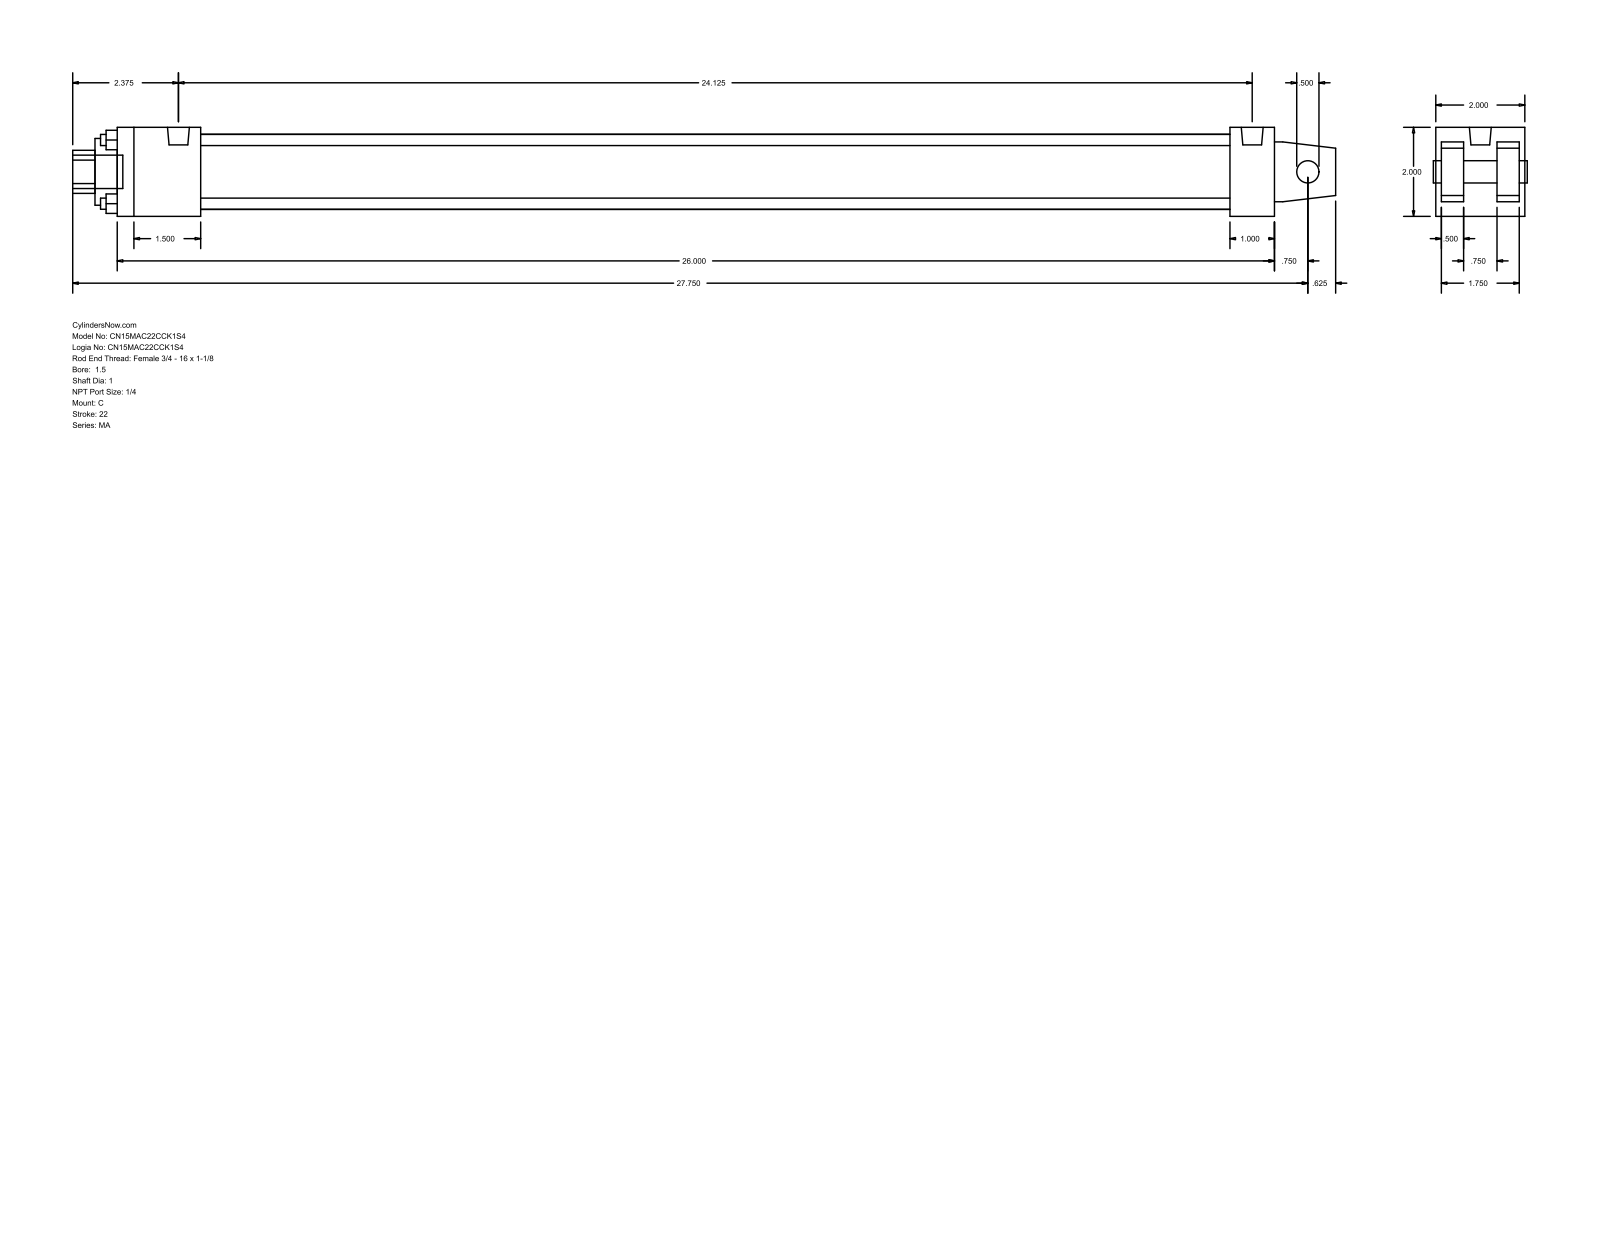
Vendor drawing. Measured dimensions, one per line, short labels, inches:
name: MA_C__0150_1
written by: GSSL Pune (CONFIG_CONTROL_DESIGN)
unit: in
bodies: 0 solids, 103 faces (76 planar, 27 cylindrical, 0 other)
size: 28.375 × 2 × 2
holes: 4× ⌀0.25, 1× ⌀0.5, 1× ⌀1, 1× ⌀1.5, 1× ⌀1.69
bosses: 4× ⌀0.313, 2× ⌀0.492, 1× ⌀0.75
rounds: 1× R0.484
face distances: 2, 1.875, 0.5, 1.375, 0.125, 0.625, 1.25, 2.375, 25.5, 1.75
hole spacings: 1.011, 1.43, 2.022
